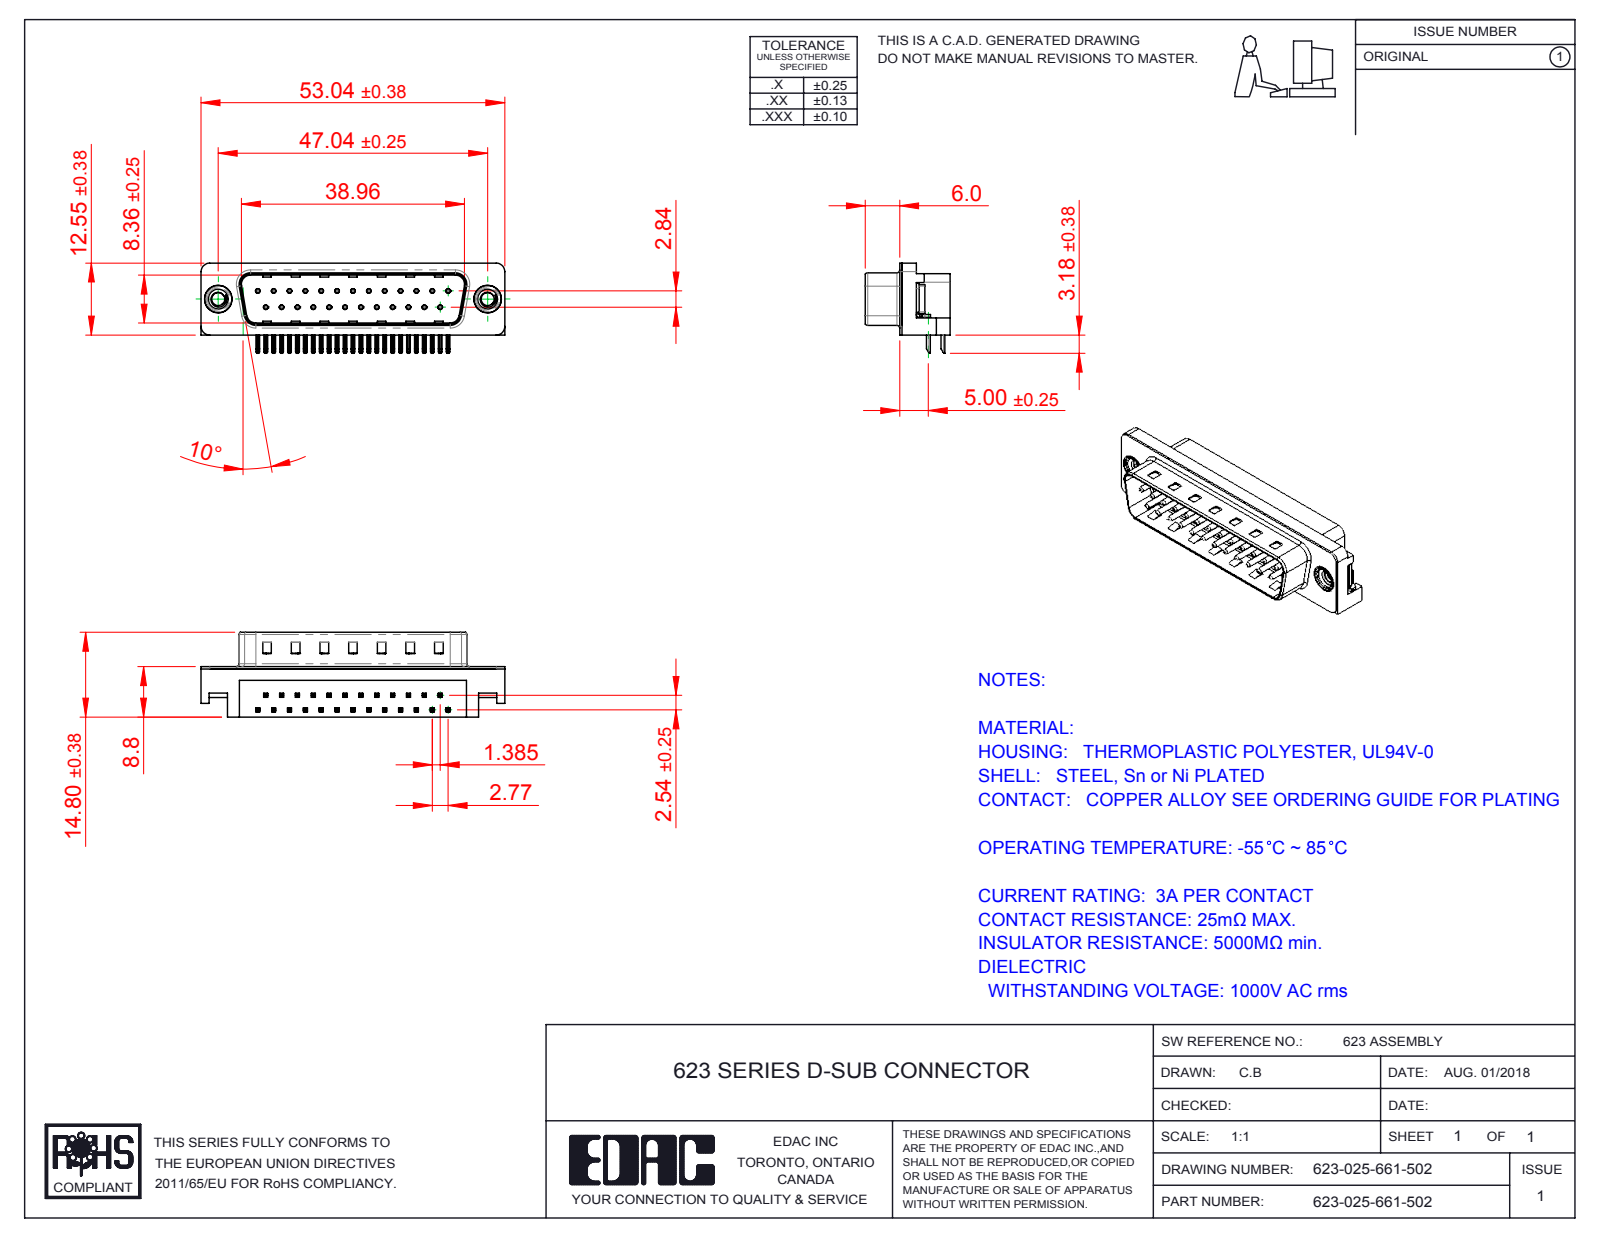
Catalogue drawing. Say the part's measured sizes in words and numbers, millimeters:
The part is named "623-025-661-502; 623 4-40 Threaded Rivet; 623 Housing_25 Socket; 623 Shell_25 Socket (+3 more)". Its 3-D file was written by "SolidWorks 2016 (CONFIG_CONTROL_DESIGN)". It is 31 solids with 2253 faces: 1405 planar, 649 cylindrical and 199 other. Overall it measures 53.04 by 15.73 by 14.8 millimeters. Its volume is 4 726 cubic millimeters and its surface area 6 717 square millimeters. Round holes: 25 of diameter 0.35, 25 of diameter 0.8, 2 of diameter 2.26, 2 of diameter 4, 2 of diameter 4.8, 2 of diameter 5. Round bosses or shafts: 25 of diameter 0.75, 2 of diameter 4.9, 2 of diameter 4.75, 2 of diameter 3.9. Partial cylindrical surfaces (rounded edges, fillets, slot ends): 108 of radius 0.25, 50 of radius 0.12, 16 of radius 1, 9 of radius 0.5, 7 of radius 1.5, 4 of radius 0.9, 4 of radius 1.6, 4 of radius 2. The main face-to-face distances are 0.4, 8.4, 2.1, 1.7, 8.76, 10.46, 10.86, 10.35, 8.8, 5.9. The hole center spacings are 3.16, 2.77, 11.08, 5.54, 8.31, 5.03, 13.85, 7.48.
